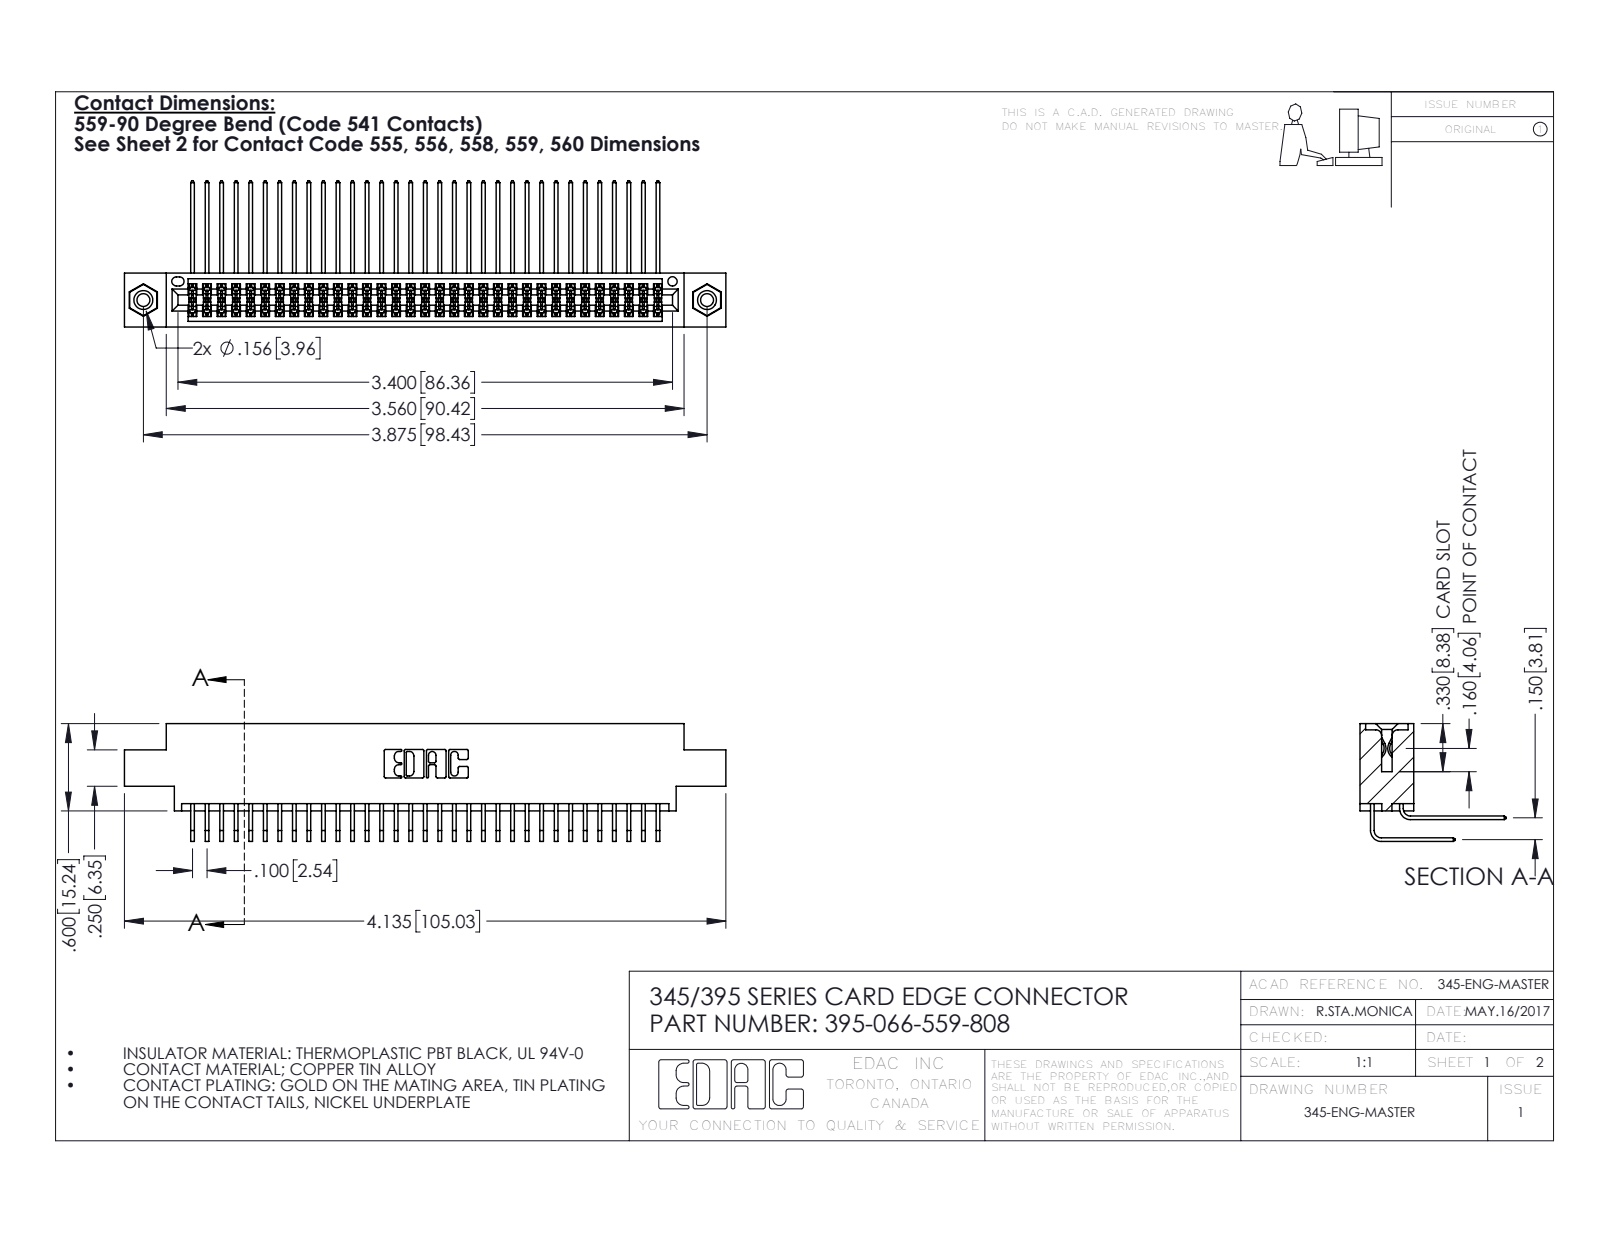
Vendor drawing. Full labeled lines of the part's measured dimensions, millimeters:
Part name (STEP PRODUCT): 345 Part_0.170 Offset - 0.156 Dia-TI; 345-292-001_559 Tail - 2; 345-292-001_558 559 Tail - 1; 395-066-559-808 (+1 more)
STEP written by: SolidWorks 2016 (CONFIG_CONTROL_DESIGN)
Units: millimetres
Bodies: 69 solids, 3622 faces (2426 planar, 1180 cylindrical, 16 other)
Overall size (bounding box): 105 × 25.5 × 20.5
Volume: 10 400 mm³ · Surface area: 17 120 mm²
Round holes (diameter × count): ⌀2.3 ×2, ⌀3.2 ×2, ⌀4 ×2, ⌀1.6 ×1
Round bosses / shafts (diameter × count): ⌀3.9 ×2
Partial cylindrical surfaces — rounded edges, fillets, slot ends (radius × count): R0.2 ×100, R0.3 ×22, R0.2 ×6, R0.8 ×6, R0.7 ×3, R0.4 ×2, R0.5 ×2, R0.6 ×2
Main face-to-face distances: 1.8, 7.6, 9.4, 5.1, 2.5, 6.9, 0.6, 5.7, 4.4, 3.8
Hole centre spacings: 6.9, 92.5, 98.4
